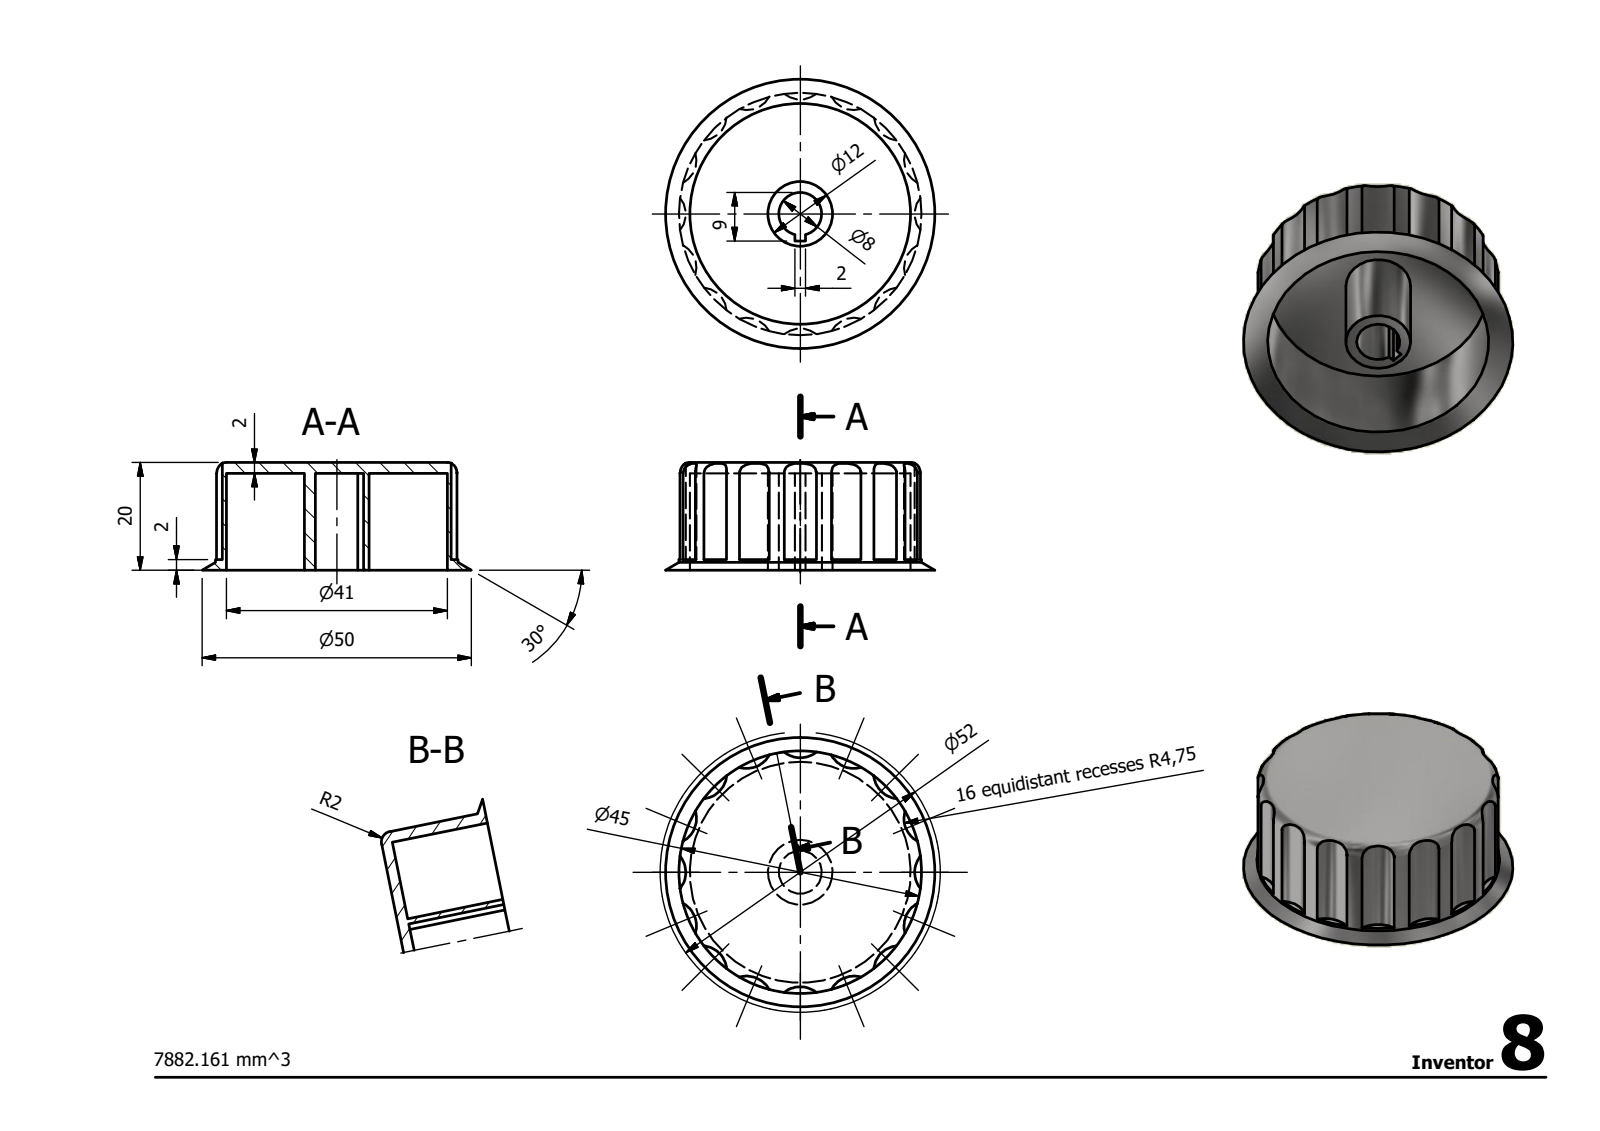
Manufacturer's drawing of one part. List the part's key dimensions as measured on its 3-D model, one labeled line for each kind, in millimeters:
STEP written by: Autodesk Inventor 2014 (AUTOMOTIVE_DESIGN)
Units: millimetres
Bodies: 1 solid, 46 faces (24 planar, 20 cylindrical, 2 other)
Overall size (bounding box): 50 × 50 × 20
Volume: 7 886 mm³ · Surface area: 10 154 mm²
Round holes (diameter × count): ⌀8 ×1, ⌀41 ×1
Round bosses / shafts (diameter × count): ⌀45 ×1, ⌀12 ×1
Partial cylindrical surfaces — rounded edges, fillets, slot ends (radius × count): R4.75 ×16
Main face-to-face distances: 2, 18, 20, 16
